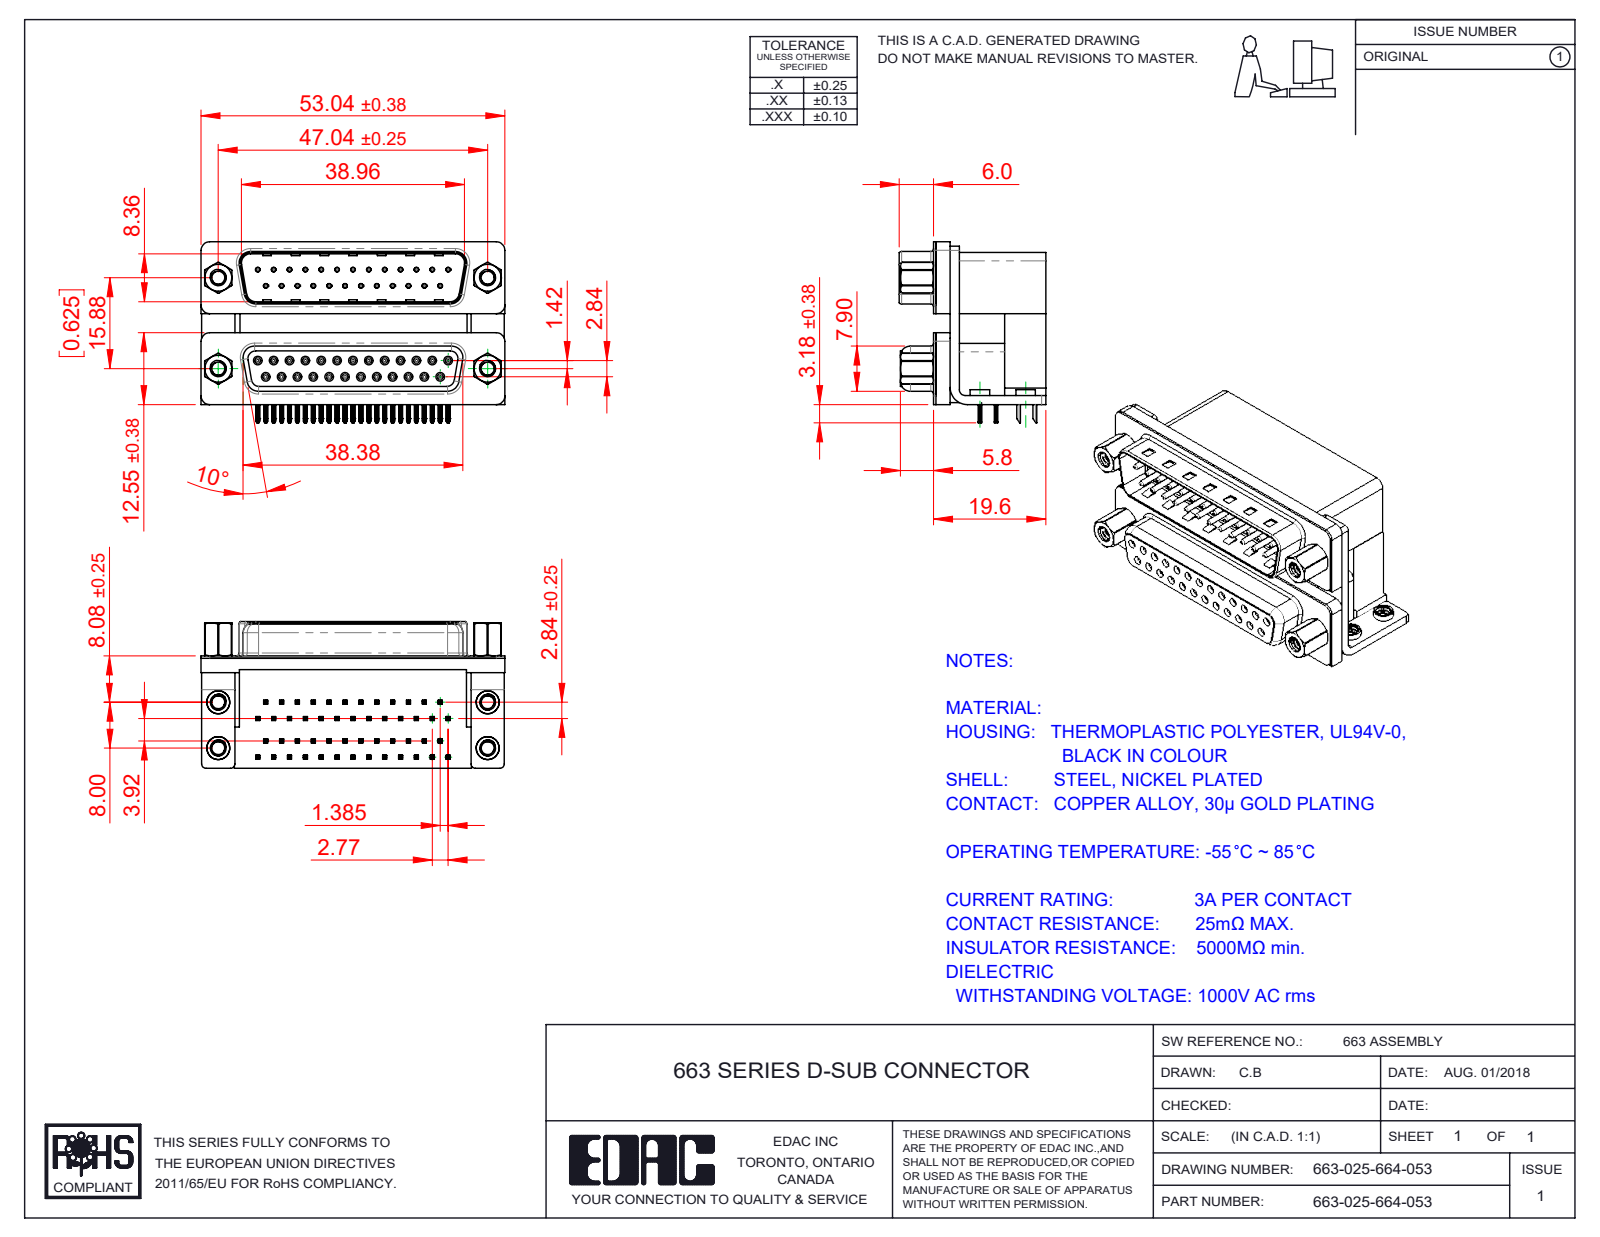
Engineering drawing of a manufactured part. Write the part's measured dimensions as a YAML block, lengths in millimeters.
part_name: "663 Mounting Bracket_ThruL; 663 4-40 Hex Standoff 5; 663 Contact Bottom Upper_L; 663 Housing Lower_25 Contacts (+8 more)"
step_written_by: "SolidWorks 2020 (CONFIG_CONTROL_DESIGN)"
units: millimeters
bodies: {solids: 69, faces: 6595, planar: 3313, cylindrical: 1763, other: 1519}
overall_size: [53.04, 31.61, 25.6]
volume: 22087
surface_area: 24247
round_holes:
  - {diameter: 0.8, count: 50}
  - {diameter: 0.35, count: 25}
  - {diameter: 0.9, count: 25}
  - {diameter: 2.26, count: 8}
  - {diameter: 2.29, count: 4}
  - {diameter: 2.75, count: 4}
  - {diameter: 3.2, count: 4}
  - {diameter: 3.5, count: 4}
  - {diameter: 4, count: 4}
  - {diameter: 4.8, count: 4}
  - {diameter: 5, count: 4}
round_bosses_or_shafts:
  - {diameter: 1.2, count: 25}
  - {diameter: 0.75, count: 25}
  - {diameter: 4.9, count: 4}
  - {diameter: 4.75, count: 4}
  - {diameter: 4, count: 4}
  - {diameter: 3.9, count: 4}
  - {diameter: 3.4, count: 4}
  - {diameter: 2.79, count: 4}
partial_cylinders:
  - {radius: 0.1, count: 200}
  - {radius: 0.15, count: 100}
  - {radius: 0.25, count: 100}
  - {radius: 0.12, count: 50}
  - {radius: 0.35, count: 50}
  - {radius: 0.34, count: 25}
  - {radius: 1.5, count: 13}
  - {radius: 0.28, count: 12}
face_to_face_distances: [0.4, 19.2, 7.2, 12, 10.7, 16.7, 9.5, 2.5, 15.53, 2.9]
hole_center_spacings: [3.16, 2.77, 5.54, 11.08, 8.31, 5.03, 13.85, 7.48]
